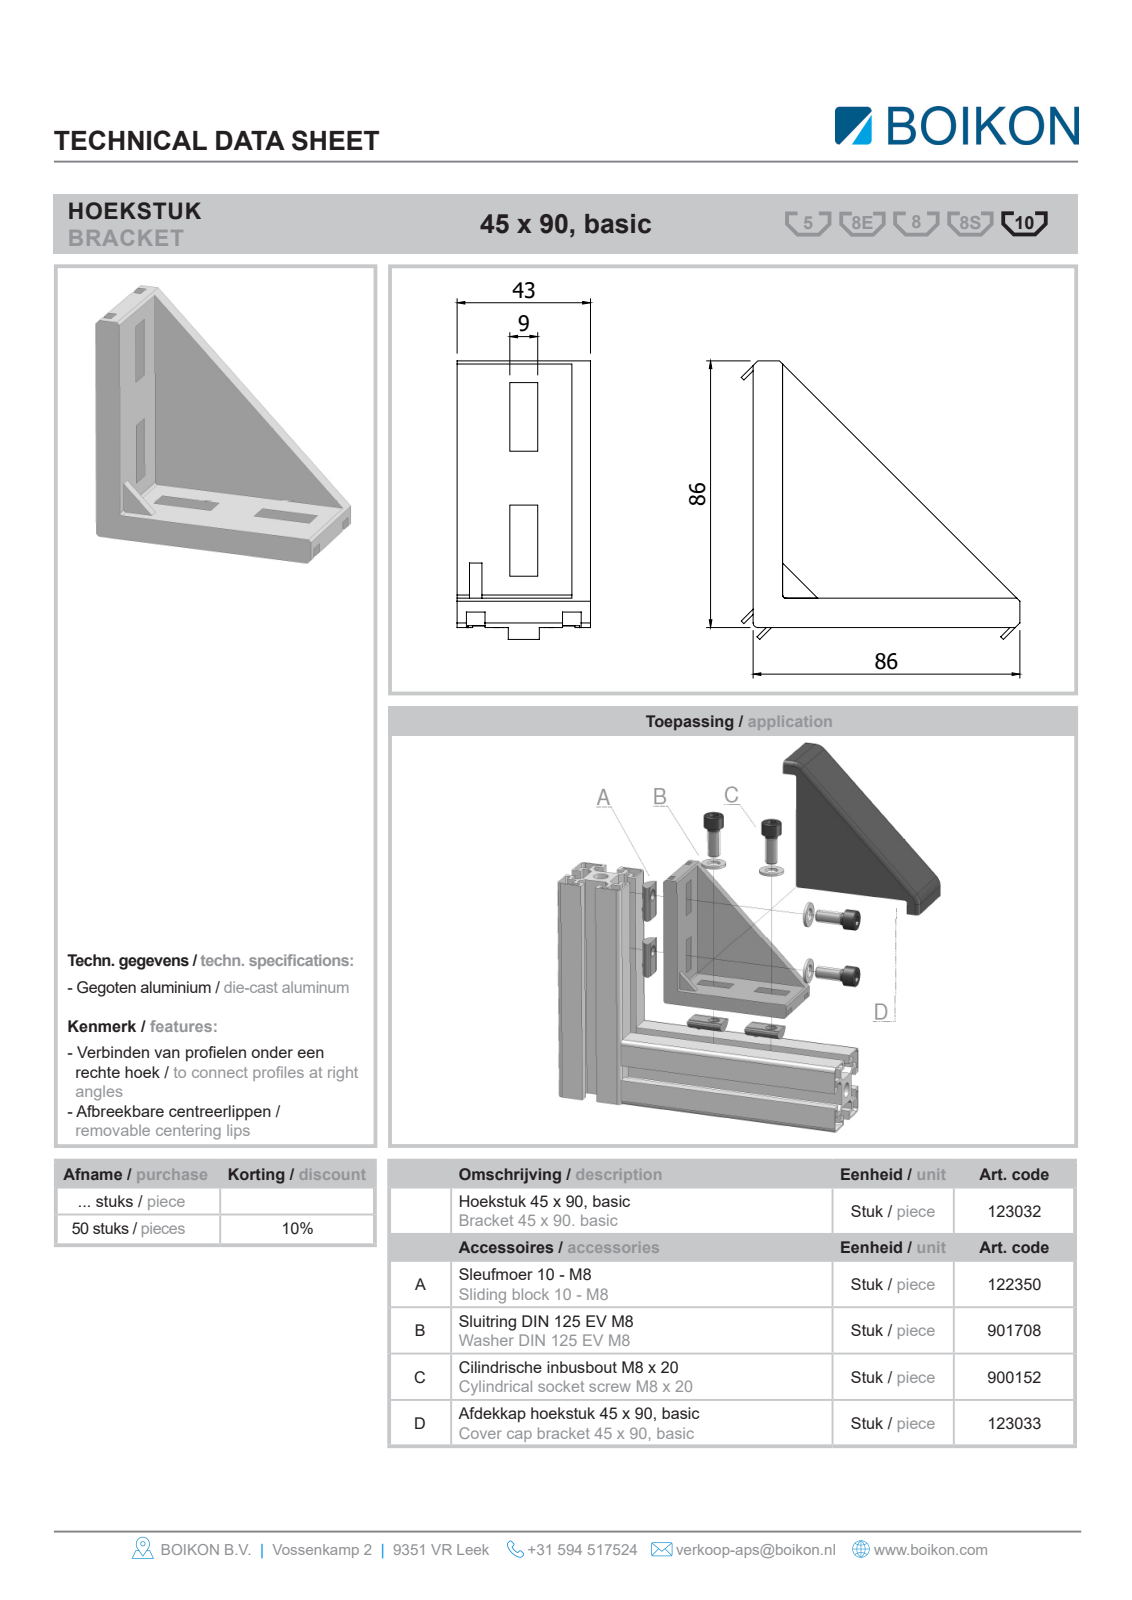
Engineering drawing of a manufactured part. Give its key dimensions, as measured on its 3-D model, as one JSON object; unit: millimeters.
{"part_name": "Root; 123032HOEKSTUK 45X90 BASICBOIKON; 123033AFDEKKAP HOEKSTUK 45X90 BASICBOIKON; 900152Cil. inbusbout DIN 912 EV M8 x 20BOIKON0 (+2 more)", "step_written_by": "HiCAD 2013 1802.4 Build 509 (AUTOMOTIVE_DESIGN)", "units": "millimeters", "bodies": {"solids": 14, "faces": 318, "planar": 254, "cylindrical": 44, "other": 20}, "overall_size": [107.89, 107.89, 43], "volume_mm3": 98649, "surface_area_mm2": 58901, "round_holes": [[8, 4], [8.4, 4]], "round_bosses_or_shafts": [[16, 4], [13, 4], [6.47, 4]], "partial_cylinders_radius": [[3, 6], [6, 2], [8, 2], [9, 2], [1, 1], [1.5, 1]], "face_to_face_distances": [43, 3, 2.2, 40.8, 5, 26, 6, 34.8, 37, 3.5], "hole_center_spacings": [39.5, 40.31]}
